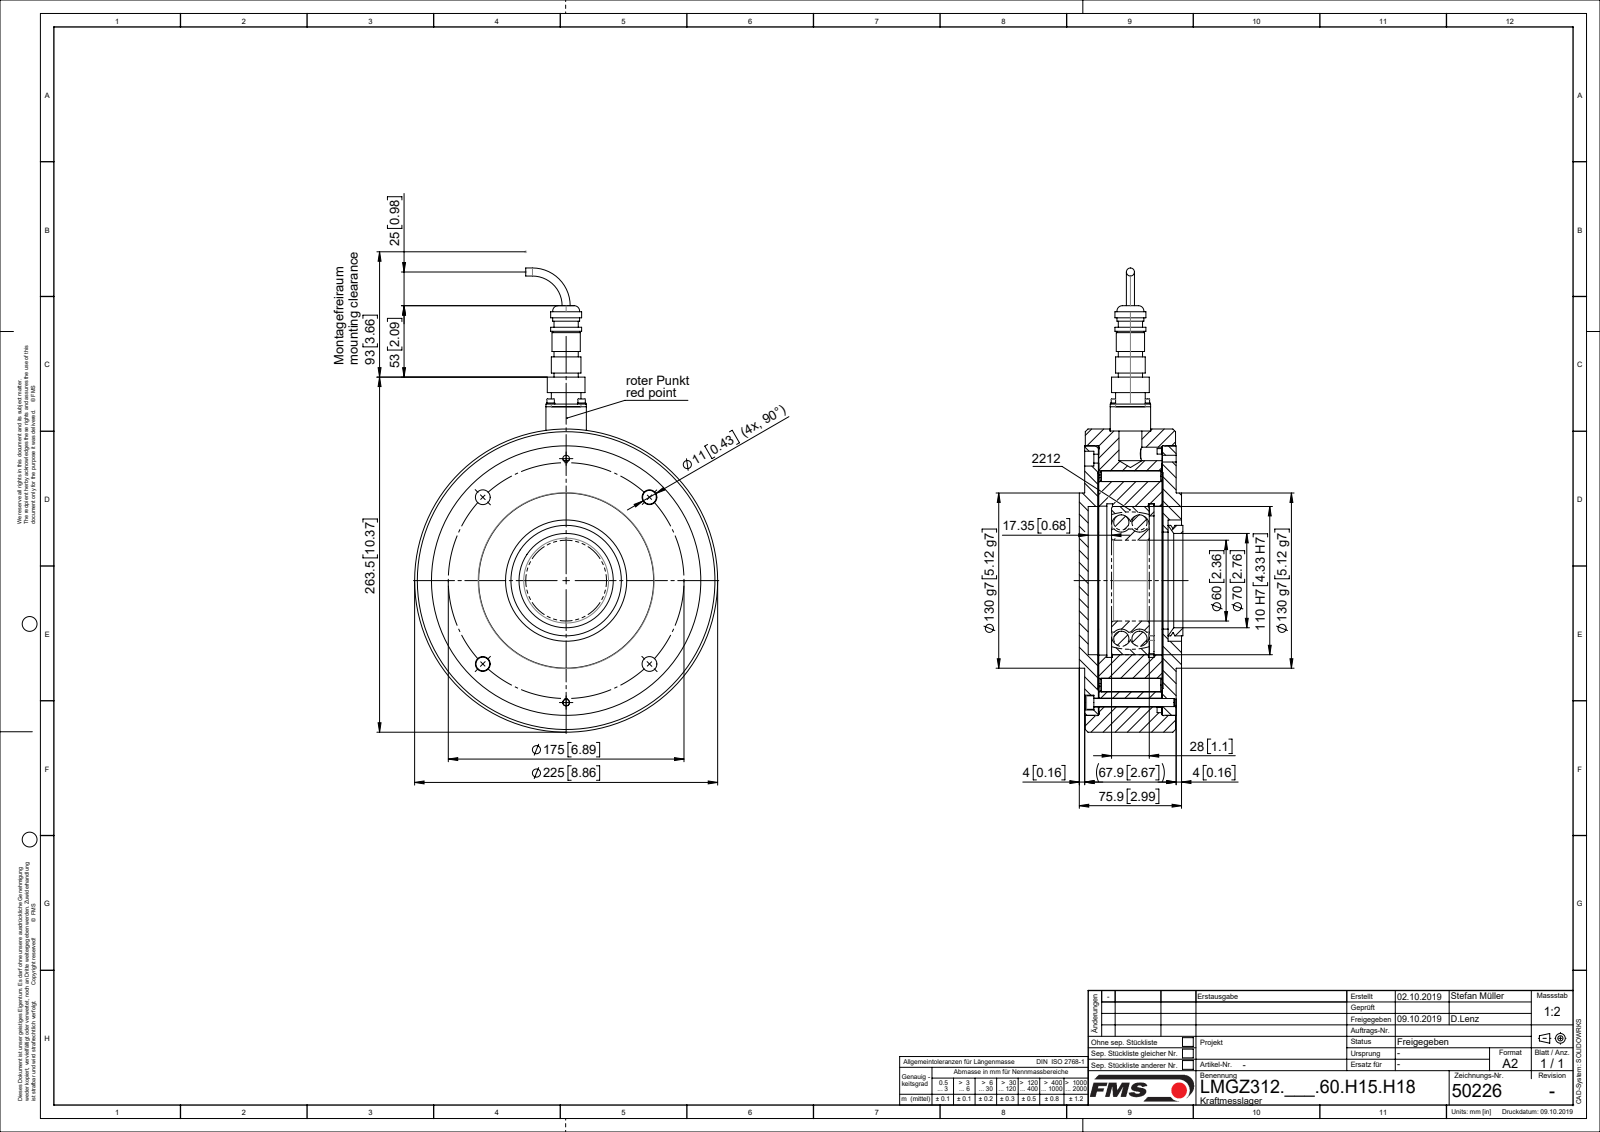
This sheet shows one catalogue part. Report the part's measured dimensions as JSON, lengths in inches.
{"part_name": "ZEICHNUNG7; L50226; L49151; TEIL1 (+8 more)", "step_written_by": "Mechanical Desktop 2007 (CONFIG_CONTROL_DESIGN)", "units": "inches", "bodies": {"solids": 19, "faces": 374, "planar": 96, "cylindrical": 226, "other": 52}, "overall_size": [13.563, 8.858, 3.028], "volume_in3": 145.5, "surface_area_in2": 605.3, "round_holes": [[0.433, 6], [0.102, 4], [0.126, 4], [0.134, 4], [0.354, 4], [0.197, 2], [0.26, 2], [2.362, 1], [2.756, 1], [2.835, 1], [3.472, 1], [3.543, 1]], "round_bosses_or_shafts": [[0.244, 4], [0.217, 4], [0.118, 4], [0.098, 4], [0.236, 2], [8.858, 1], [7.835, 1], [5.118, 1]], "partial_cylinders_radius": [[0.157, 4], [3.189, 1], [3.386, 1]], "face_to_face_distances": [1.86, 0.411, 2.272, 0.402, 2.262, 1.87, 0.384, 0.382, 2.291, 0.02], "hole_center_spacings": [0.906, 2.684, 3.445, 4.872, 6.474, 1.281, 3.563, 6.889]}
